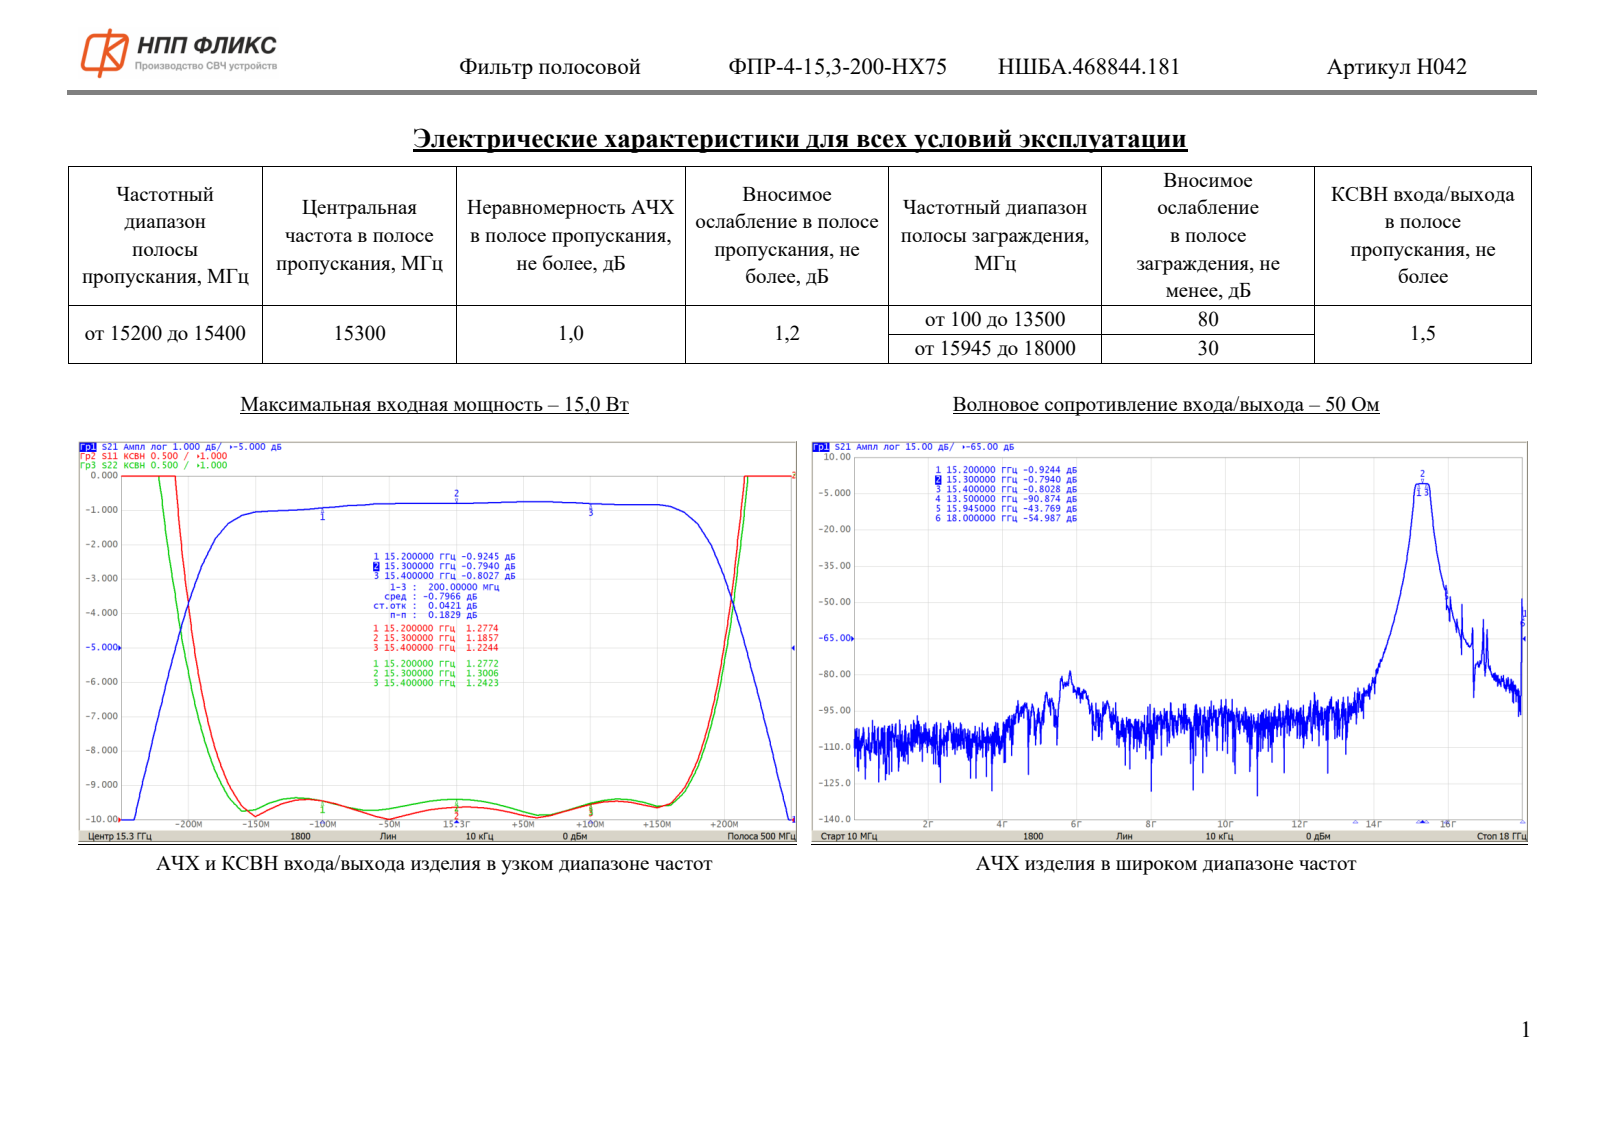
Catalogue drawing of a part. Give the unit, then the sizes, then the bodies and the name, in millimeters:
Units: millimetres
Overall size (bounding box): 67.2 × 38.1 × 38.1
Round holes (diameter × count): ⌀2.05 ×14, ⌀2.6 ×14, ⌀2.7 ×14, ⌀1.25 ×9, ⌀3.7 ×4, ⌀2 ×2
Round bosses / shafts (diameter × count): ⌀5 ×14, ⌀3.8 ×14, ⌀2.5 ×14, ⌀1.6 ×9
Partial cylindrical surfaces — rounded edges, fillets, slot ends (radius × count): R3 ×4, R0.4 ×3, R0.2 ×1, R0.6 ×1, R0.7 ×1
Main face-to-face distances: 4.3, 62.9, 14.1, 67.2, 58.6, 29, 14.3, 23.8, 38.1, 4.55
Hole centre spacings: 8.8, 25, 17.6, 26.4, 29.28, 35.28, 23.4, 35.2
Volume: 33 748 mm³ · Surface area: 15 827 mm²
Bodies: 38 solids, 1153 faces (821 planar, 150 cylindrical, 182 other)
Part name (STEP PRODUCT): НШБА.468844.181_Фильтр ФПР-4-15,3-200-НХ75
STEP written by: ASCON Math Kernel (CONFIG_CONTROL_DESIGN)
